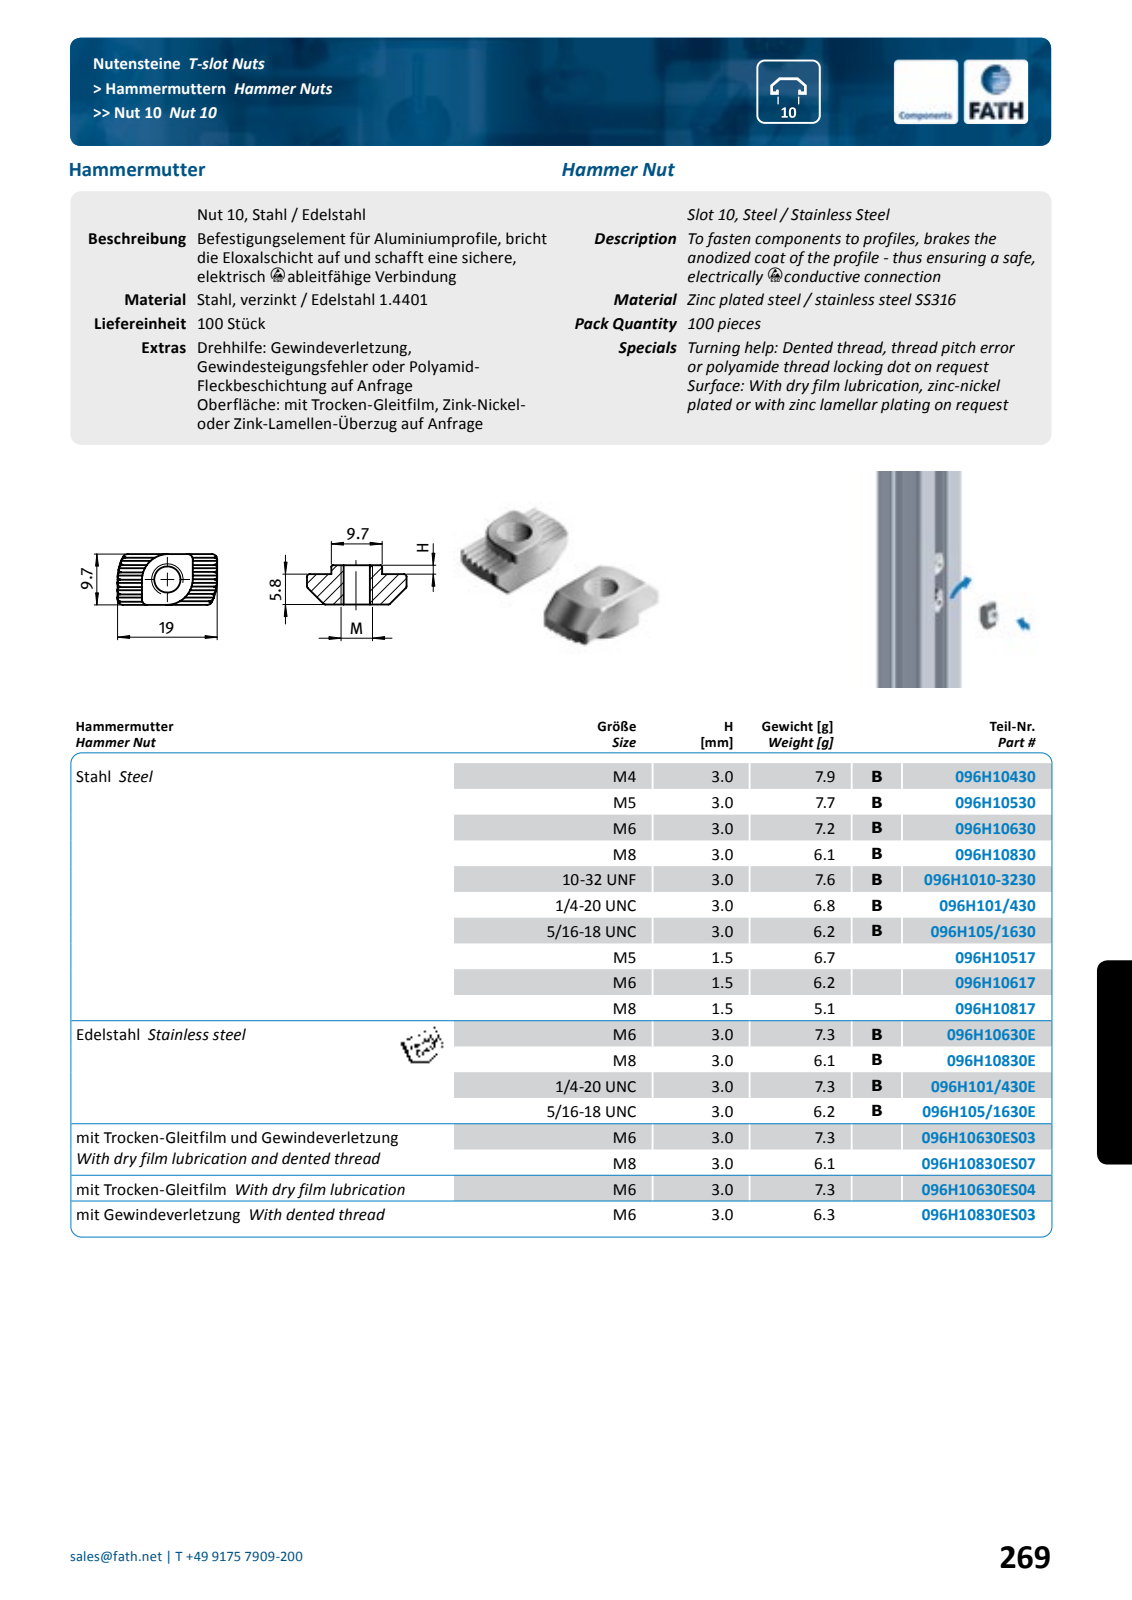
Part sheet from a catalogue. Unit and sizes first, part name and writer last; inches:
Units: inches
Overall size (bounding box): 0.748 × 0.382 × 0.346
Round holes (diameter × count): ⌀0.257 ×1
Partial cylindrical surfaces — rounded edges, fillets, slot ends (radius × count): R0.008 ×7, R0.02 ×6, R0.197 ×2, R0.374 ×1
Main face-to-face distances: 0.382, 0.039, 0.078, 0.117, 0.346, 0.156, 0.195, 0.183, 0.565, 0.234
Volume: 0.053 in³ · Surface area: 1.32 in²
Bodies: 1 solid, 80 faces (38 planar, 40 cylindrical, 2 other)
Part name (STEP PRODUCT): fath_096h105-1630e
STEP written by: Spatial InterOp 3D (automotive_design)
